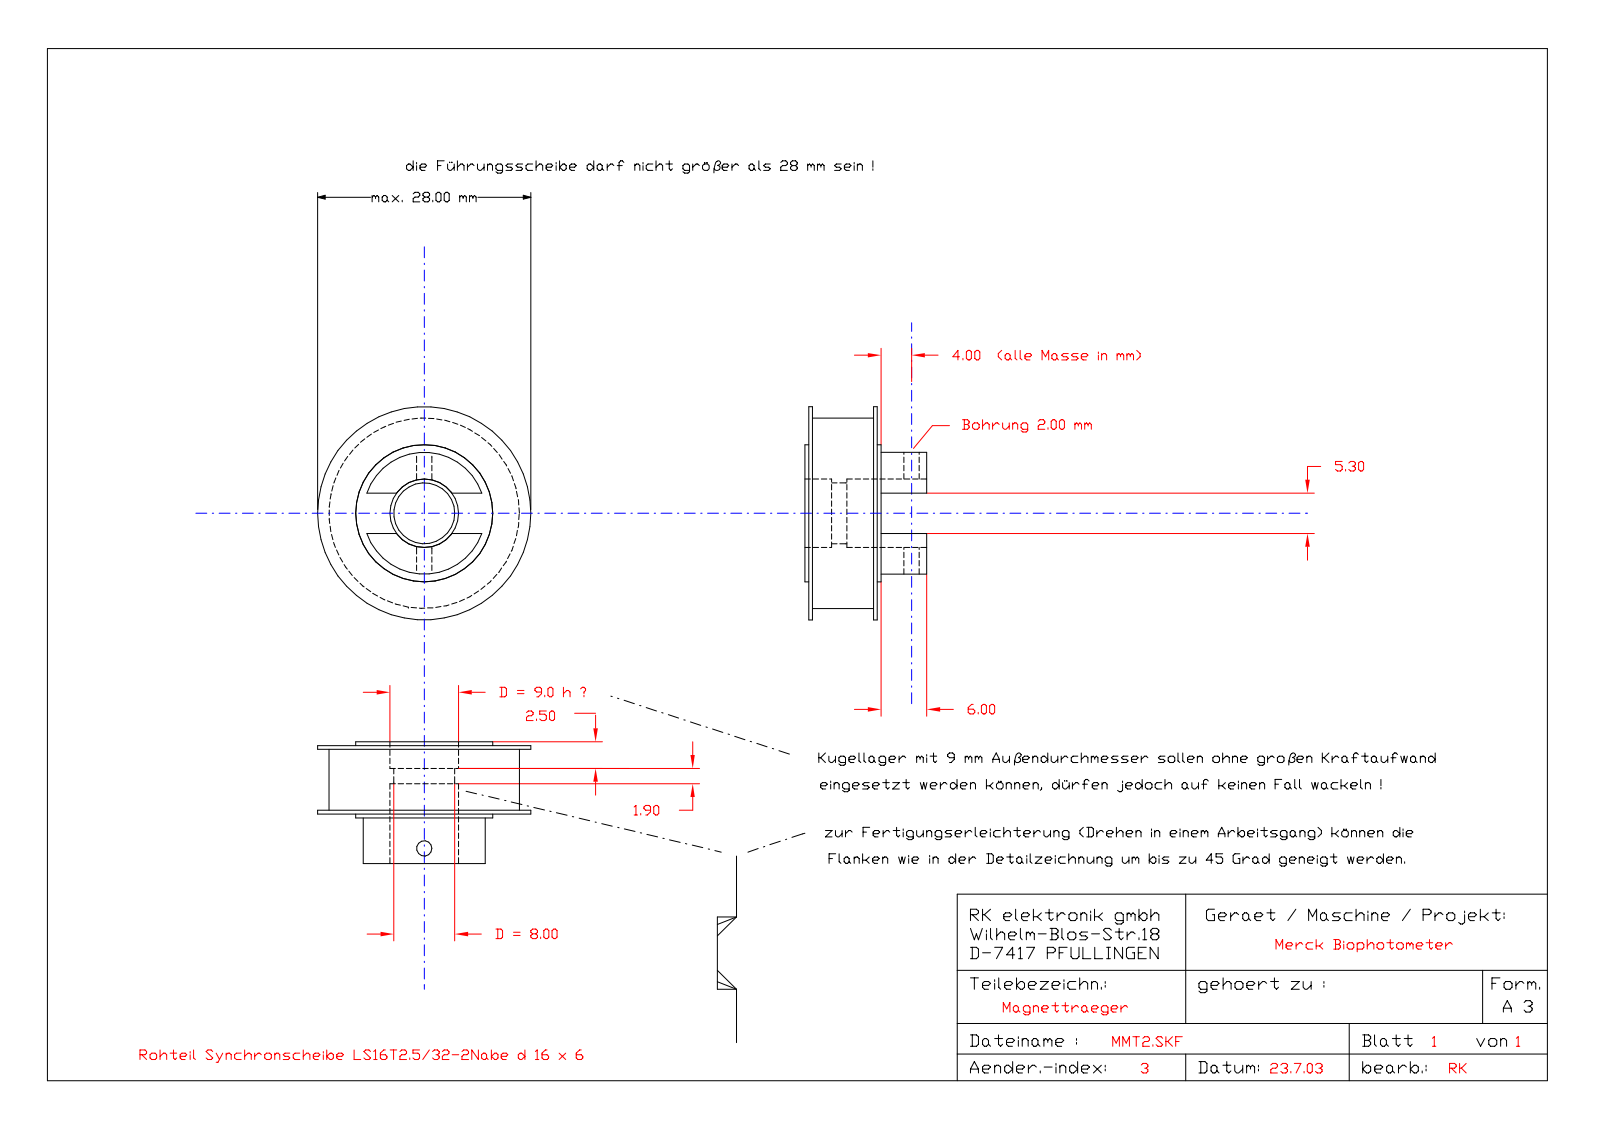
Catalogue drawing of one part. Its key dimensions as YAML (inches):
part_name: "Zahnrad"
step_written_by: "SolidWorks 2020 (CONFIG_CONTROL_DESIGN)"
units: inches
bodies: {solids: 1, faces: 197, planar: 14, cylindrical: 163, other: 20}
overall_size: [1.15, 1.15, 0.843]
volume: 0.397
surface_area: 6.522
round_holes:
  - {diameter: 0.488, count: 1}
  - {diameter: 0.709, count: 1}
round_bosses_or_shafts:
  - {diameter: 1.15, count: 1}
partial_cylinders:
  - {radius: 0.038, count: 26}
  - {radius: 0.102, count: 26}
  - {radius: 0.169, count: 26}
  - {radius: 0.235, count: 26}
  - {radius: 0.321, count: 26}
  - {radius: 0.053, count: 13}
